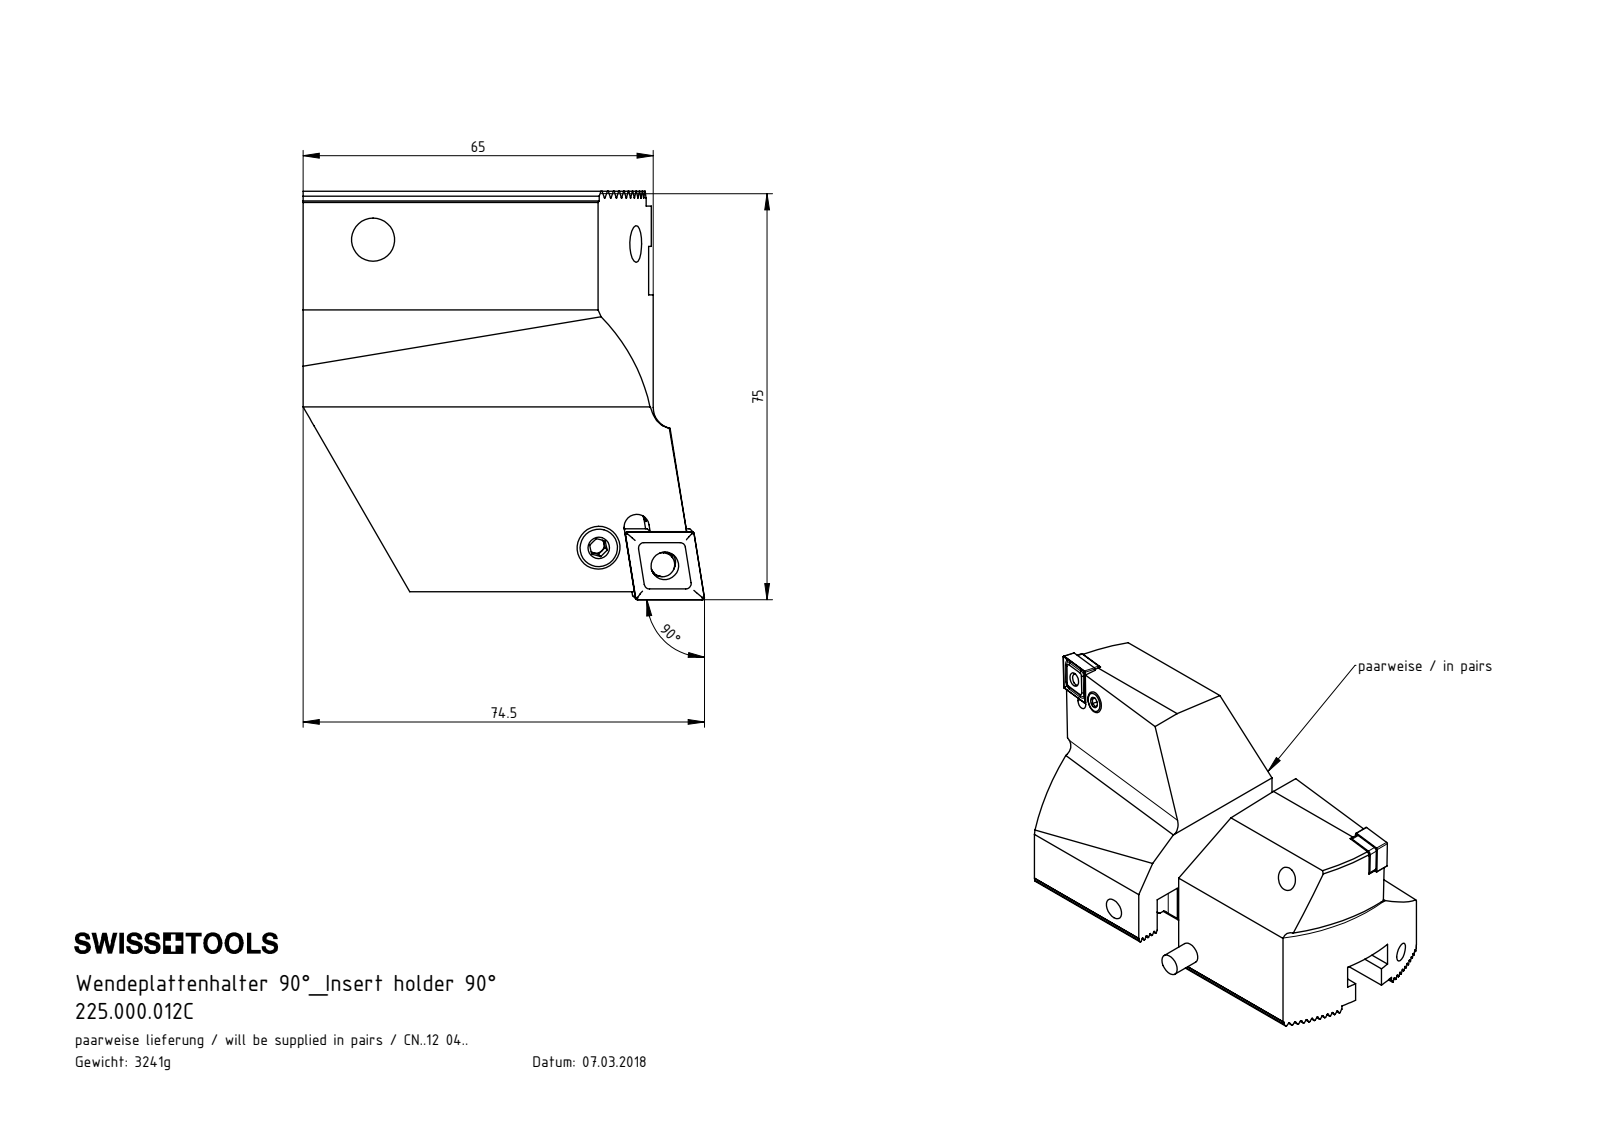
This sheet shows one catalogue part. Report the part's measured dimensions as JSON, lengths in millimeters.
{"part_name": "225.000.012C; CNMG120404; ISO 8734 - 8 x 20 m6; WCD-ER4.101.017_A (+6 more)", "step_written_by": "SolidWorks 2017 (CONFIG_CONTROL_DESIGN)", "units": "millimeters", "bodies": {"solids": 16, "faces": 1263, "planar": 759, "cylindrical": 164, "other": 340}, "overall_size": [205.01, 94, 75.79], "volume_mm3": 413723, "surface_area_mm2": 67086, "round_holes": [[8, 4], [5.16, 2], [6.4, 2], [6.8, 2], [7, 2], [8.4, 2]], "round_bosses_or_shafts": [[8, 3], [7.9, 2], [6.4, 2], [4.5, 2], [3.55, 2], [5.5, 1]], "partial_cylinders_radius": [[0.14, 22], [0.4, 8], [1, 8], [2.5, 6], [2.1, 2], [2.2, 2], [2.35, 2], [2.8, 2]], "face_to_face_distances": [1.73, 8.66, 3.46, 70, 6.93, 5.2, 43.3, 24.5, 45.5, 10.39], "hole_center_spacings": [7, 12.8, 12.86, 75, 40, 68, 82]}
